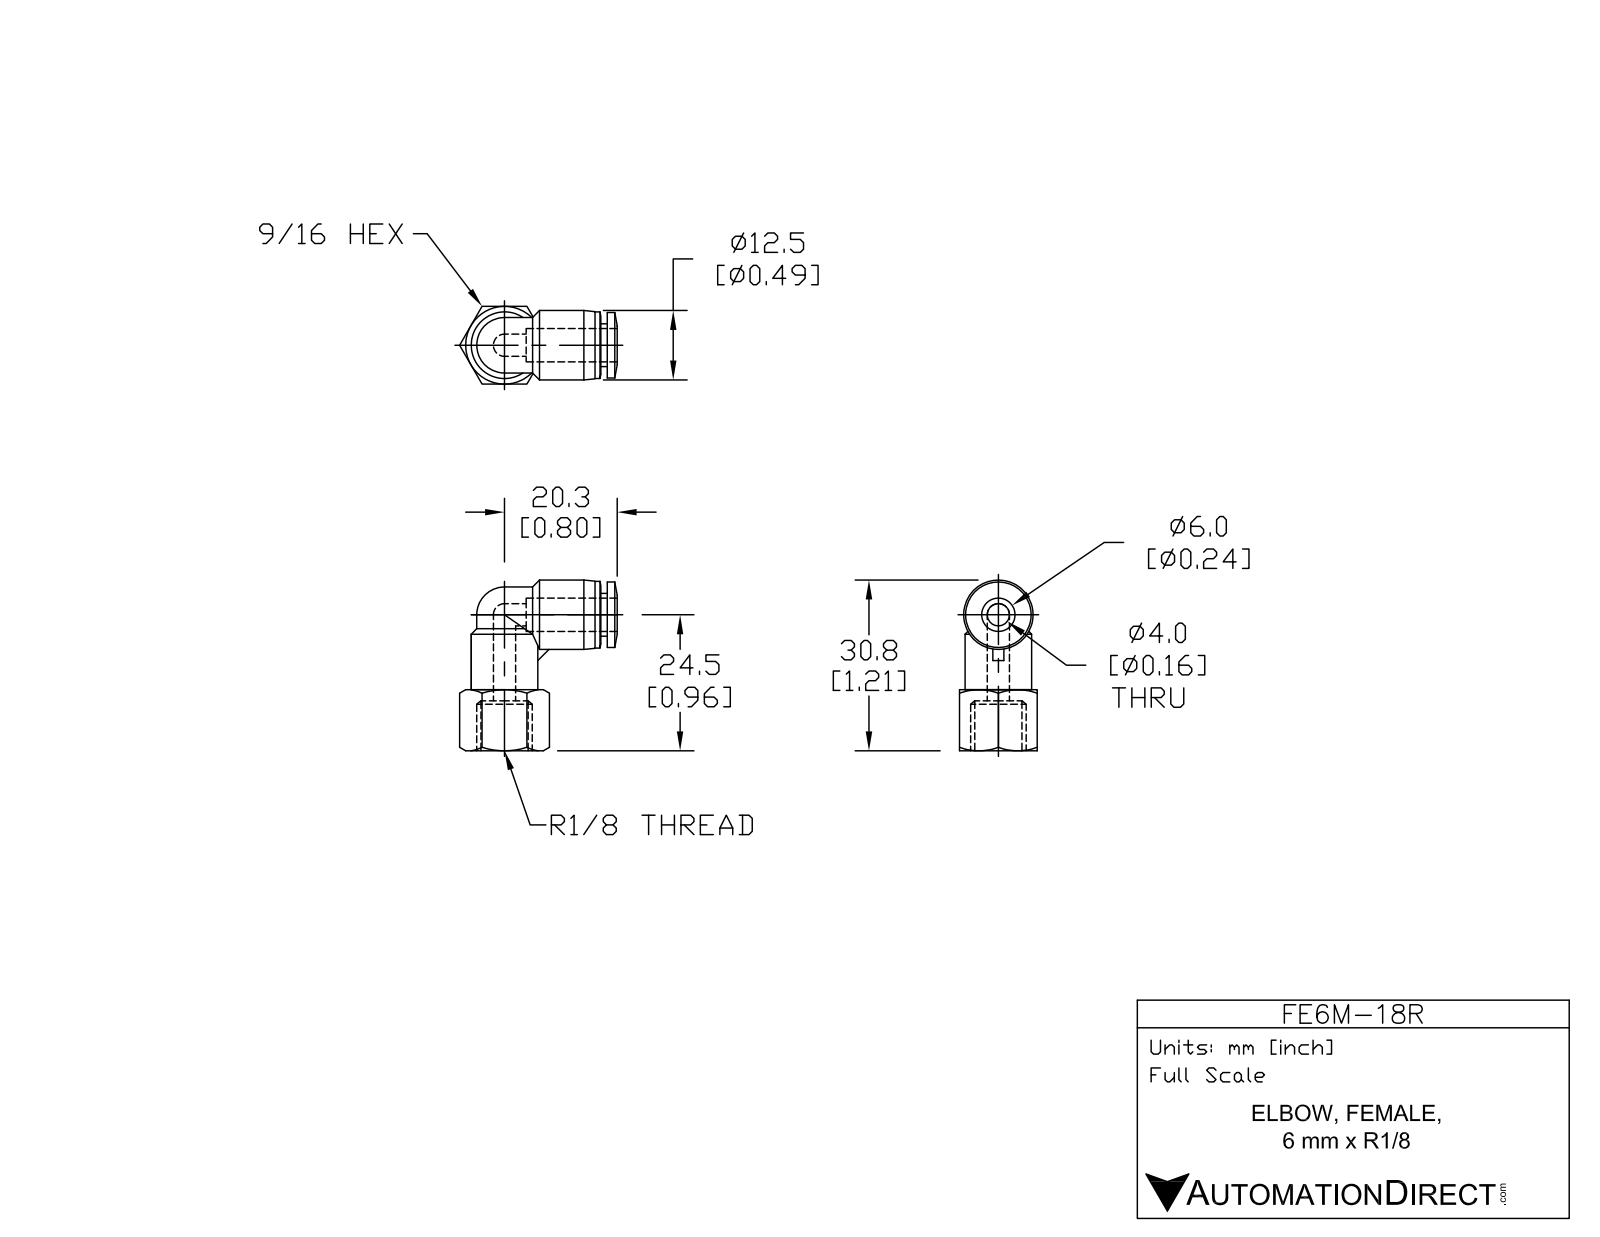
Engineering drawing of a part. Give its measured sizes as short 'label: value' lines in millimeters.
name: FE6M-18R
written by: SolidWorks 2015 (AUTOMOTIVE_DESIGN)
unit: mm
bodies: 1 solid, 67 faces (17 planar, 19 cylindrical, 31 other)
size: 30.8 × 28.4 × 14
volume: 3 950 mm³; area: 2 973 mm²
holes: 2× ⌀4, 1× ⌀6.3
bosses: 2× ⌀12, 1× ⌀12.5, 1× ⌀11.8, 1× ⌀7.7
rounds: 2× R5
face distances: 14, 9, 2, 11, 1.1, 13.5, 14.6, 6, 8, 16.4
